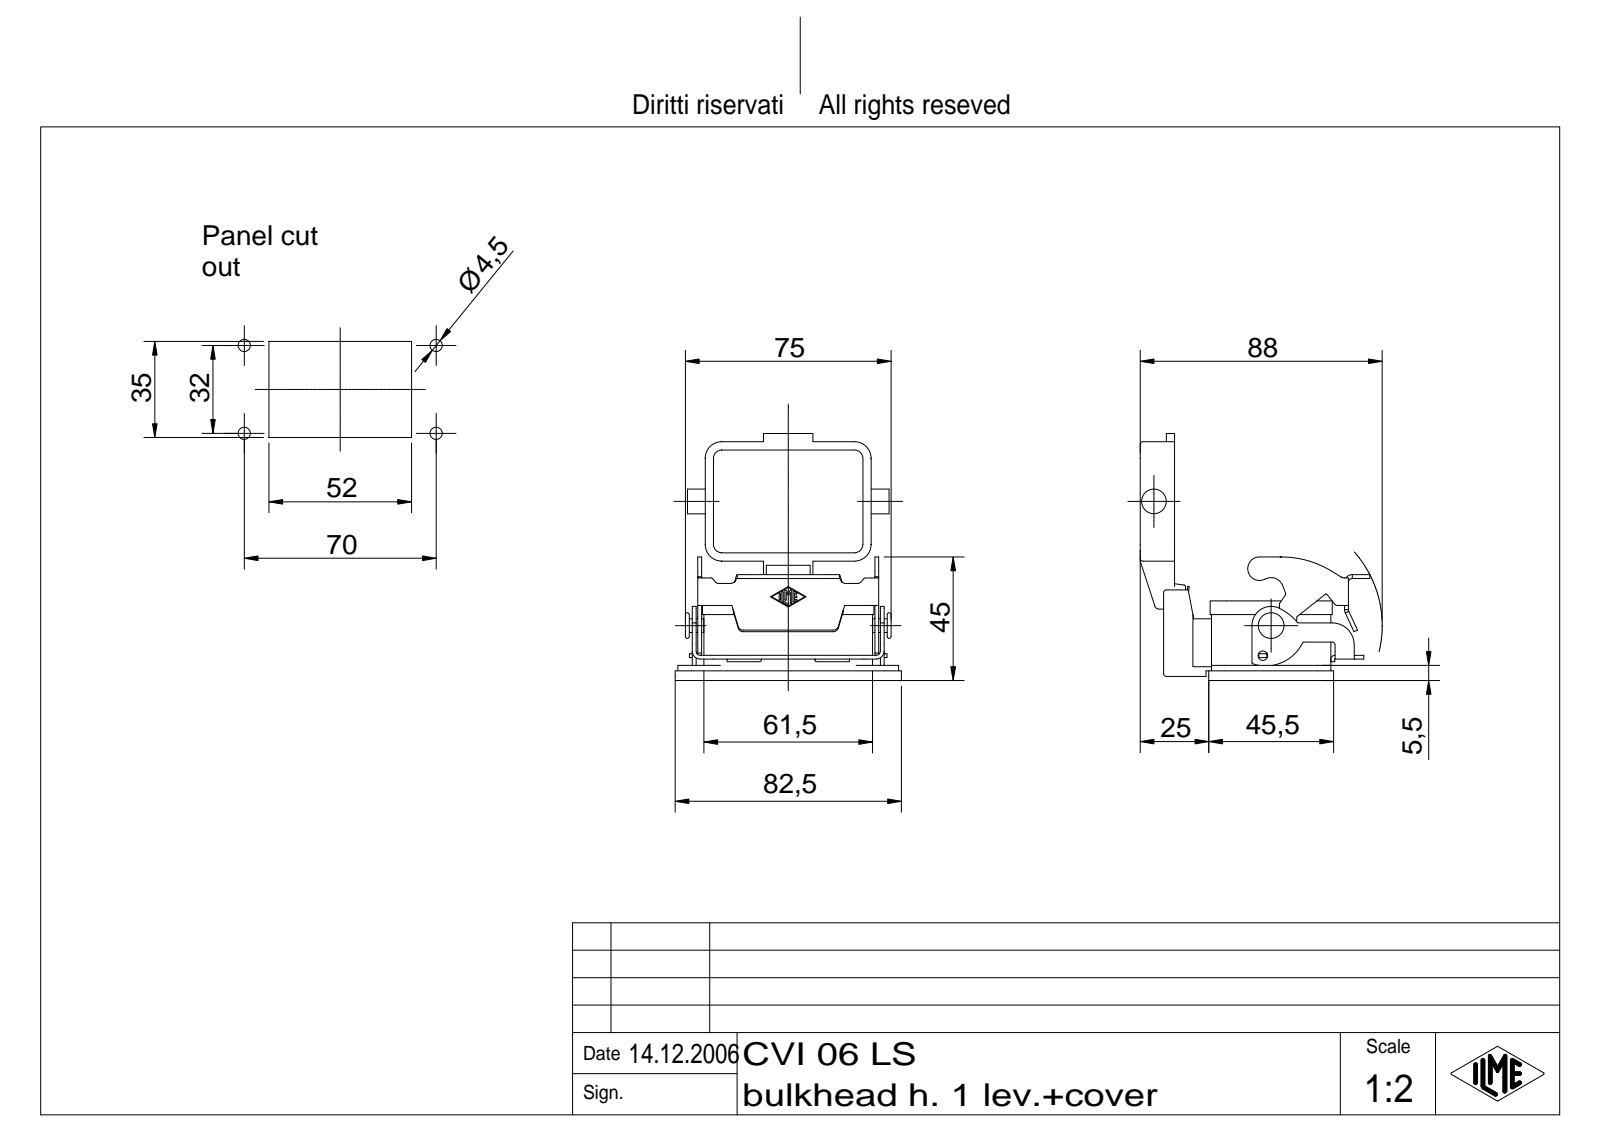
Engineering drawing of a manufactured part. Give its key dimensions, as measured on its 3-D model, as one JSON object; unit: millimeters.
{"part_name": "CVI 06 LS", "step_written_by": "Autodesk Inventor 7 (AUTOMOTIVE_DESIGN)", "units": "millimeters", "bodies": {"solids": 4, "faces": 594, "planar": 226, "cylindrical": 205, "other": 163}, "overall_size": [90, 83.73, 82.5], "volume_mm3": 53728, "surface_area_mm2": 42096, "round_holes": [[4.5, 4], [4.5, 4], [3.5, 1], [4, 1]], "round_bosses_or_shafts": [[5, 2], [9, 1], [7, 1], [3.2, 1], [3, 1]], "partial_cylinders_radius": [[1, 27], [3, 16], [6, 16], [0.25, 15], [0.5, 10], [1.5, 10], [2, 7], [1.4, 6]], "face_to_face_distances": [3, 40.5, 0.5, 4, 3.5, 58, 2.5, 2, 12.5, 29], "hole_center_spacings": [32, 70, 76.97]}
